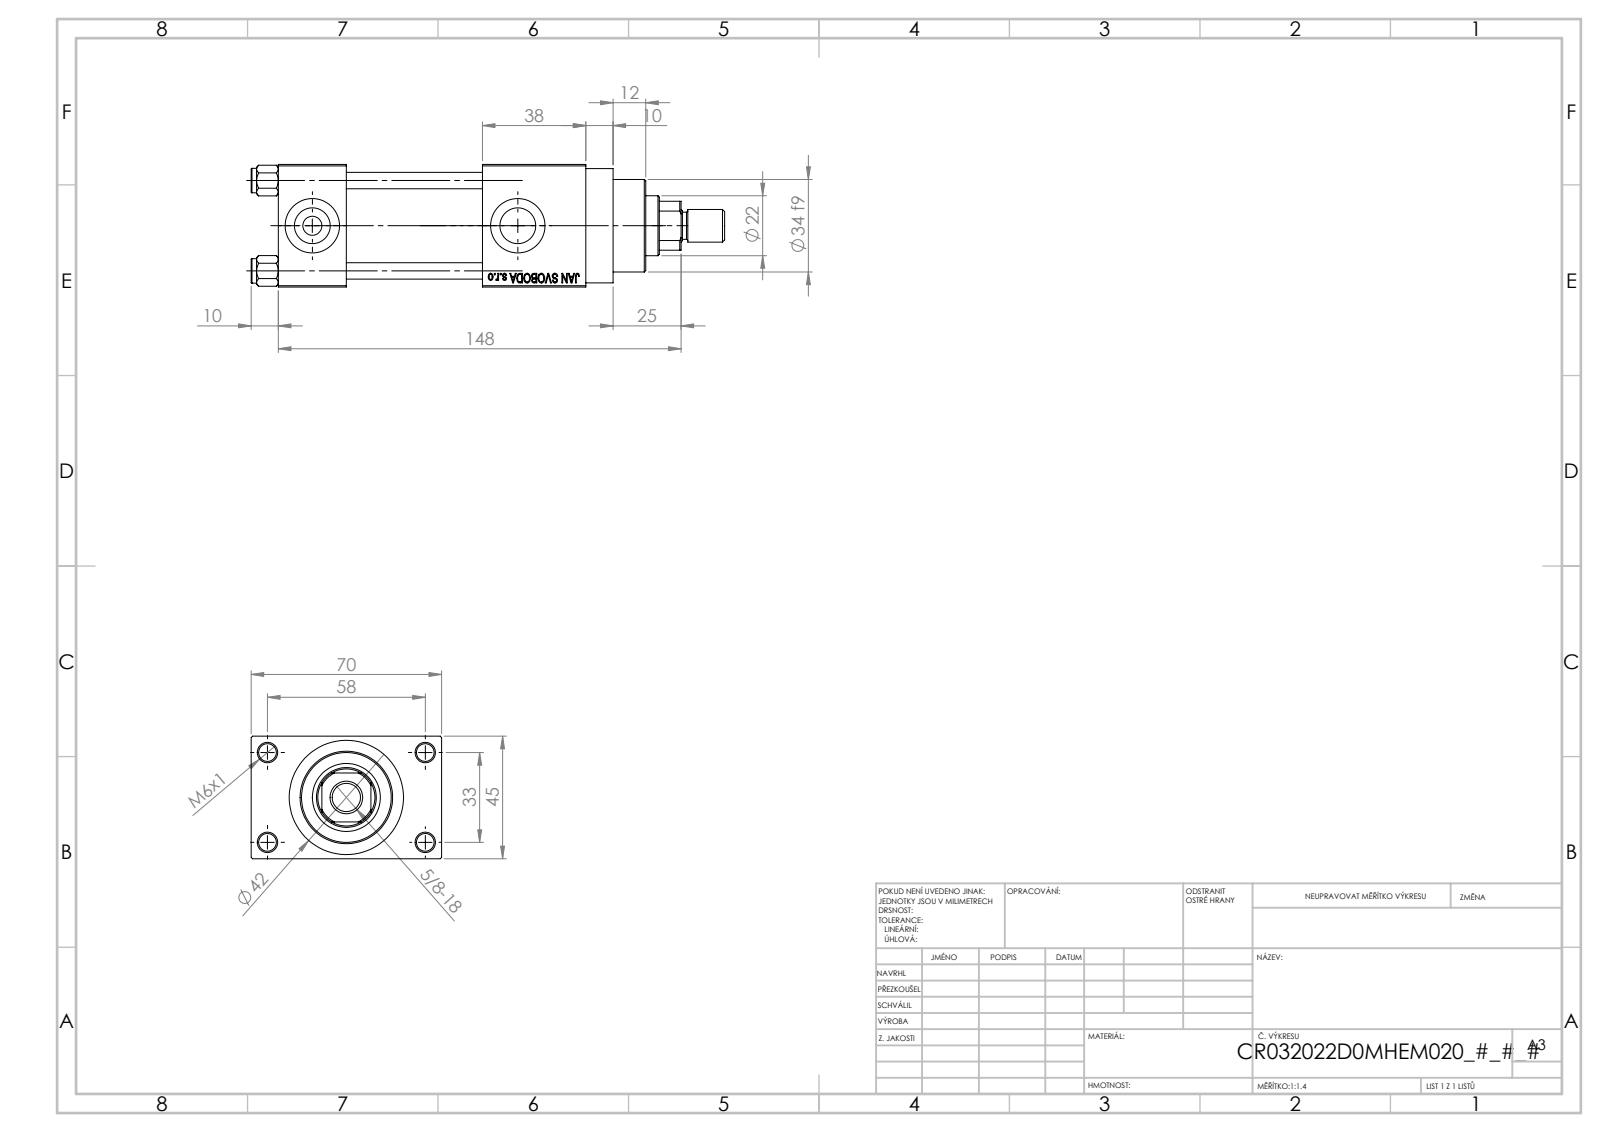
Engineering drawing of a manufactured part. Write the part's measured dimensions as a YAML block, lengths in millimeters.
part_name: "NUT_M5_D; V215CR_D_Body; V215_VC_A; V215CR_VCP_D (+2 more)"
step_written_by: "SolidWorks 2019 (CONFIG_CONTROL_DESIGN)"
units: millimeters
bodies: {solids: 12, faces: 1116, planar: 500, cylindrical: 92, other: 524}
overall_size: [174, 70, 45]
volume: 244722
surface_area: 80821
round_holes:
  - {diameter: 6, count: 4}
  - {diameter: 6.5, count: 4}
  - {diameter: 7, count: 2}
  - {diameter: 13.16, count: 2}
  - {diameter: 20, count: 2}
  - {diameter: 10.5, count: 1}
  - {diameter: 22, count: 1}
  - {diameter: 24, count: 1}
  - {diameter: 25, count: 1}
  - {diameter: 32, count: 1}
  - {diameter: 33, count: 1}
round_bosses_or_shafts:
  - {diameter: 9, count: 4}
  - {diameter: 42, count: 1}
  - {diameter: 38, count: 1}
  - {diameter: 34, count: 1}
  - {diameter: 12, count: 1}
  - {diameter: 10, count: 1}
partial_cylinders:
  - {radius: 10.5, count: 1}
face_to_face_distances: [45, 25, 50, 12.5, 75, 57.5, 88, 38, 113, 70]
hole_center_spacings: [12.4, 23.48, 33.2, 33.37, 35.35, 45.6, 56.35, 33]
